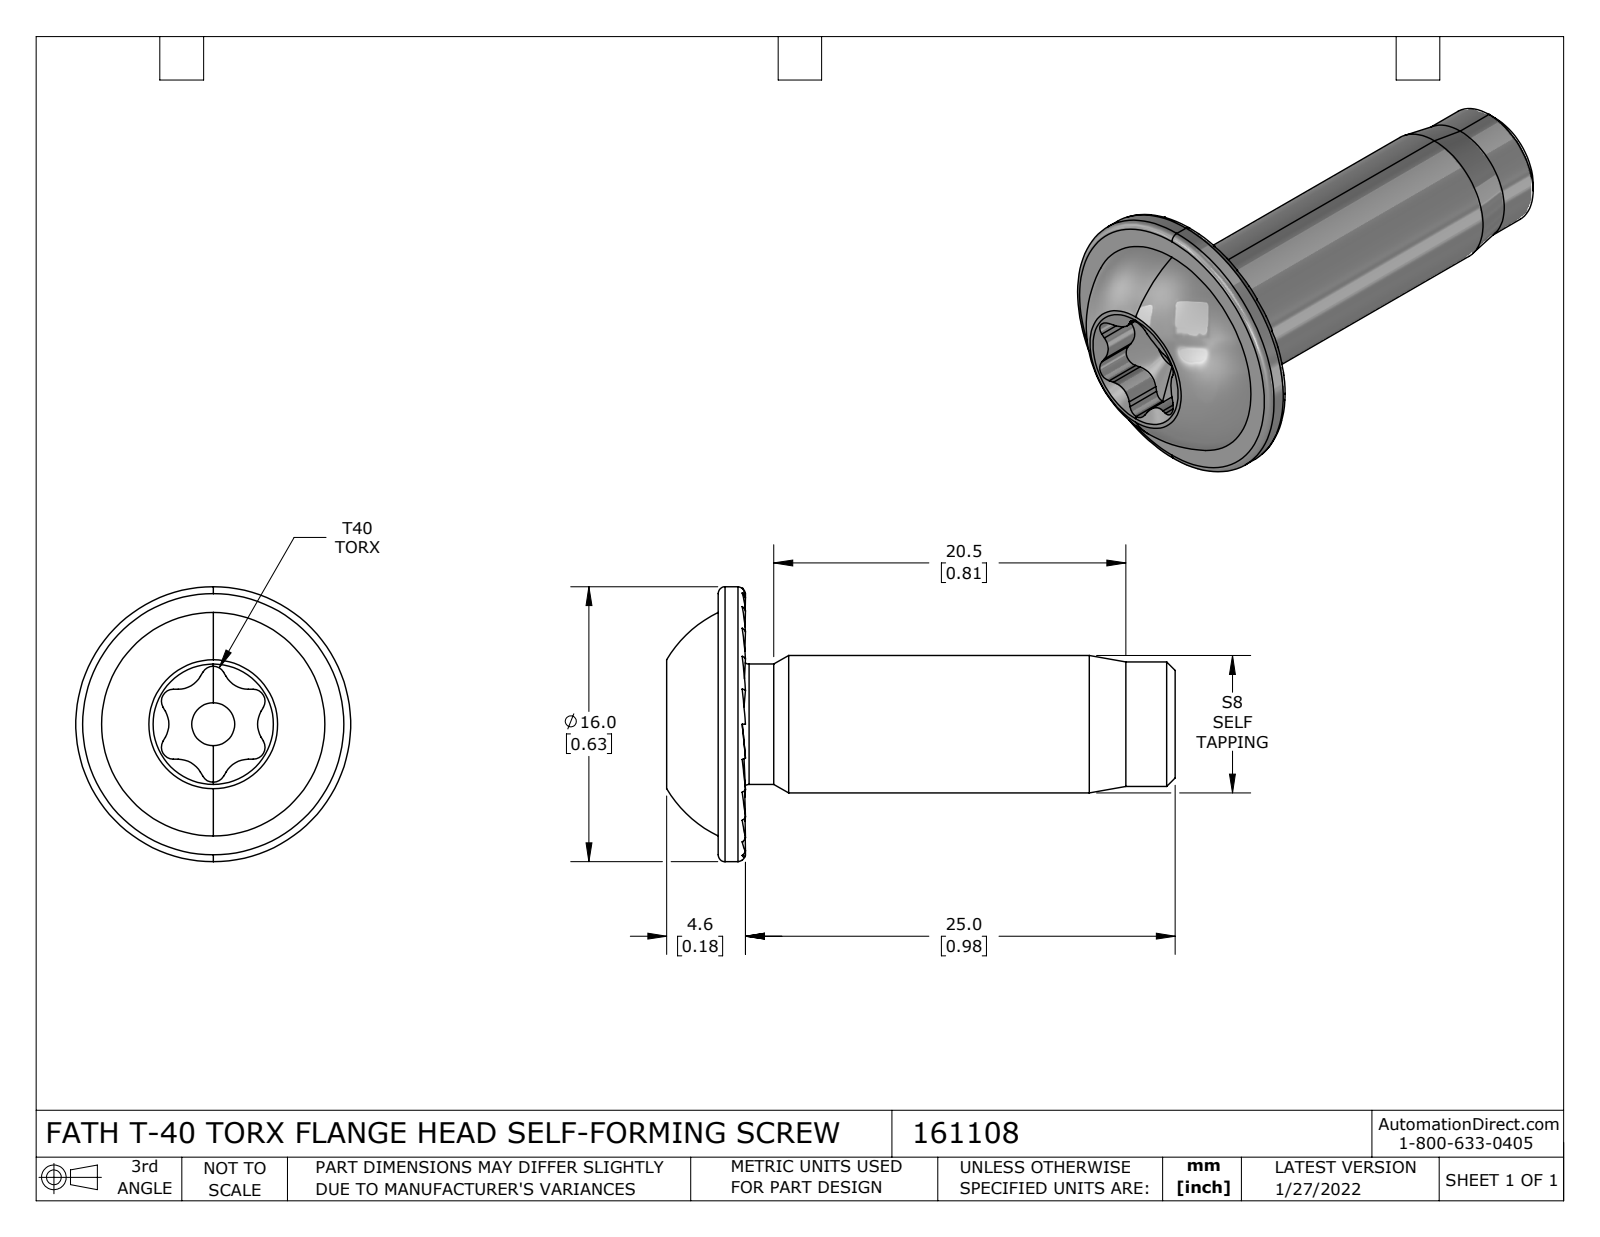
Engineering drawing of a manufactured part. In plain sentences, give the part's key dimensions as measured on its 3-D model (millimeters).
The part is named "161108". Its 3-D file was written by "SolidWorks 2021 (CONFIG_CONTROL_DESIGN)". It is 1 solid with 128 faces: 89 planar, 21 cylindrical and 18 other. Overall it measures 29.6 by 16 by 16 millimeters. Its volume is 1 698 cubic millimeters and its surface area 1 186 square millimeters. Round bosses or shafts: 1 of diameter 16, 1 of diameter 8, 1 of diameter 7.25, 1 of diameter 7. Partial cylindrical surfaces (rounded edges, fillets, slot ends): 6 of radius 0.7, 6 of radius 1.5. The main face-to-face distances are 26.6, 2.04, 29.6, 3, 4.08, 25.2, 1.4, 4.4, 25.45, 1.15.
